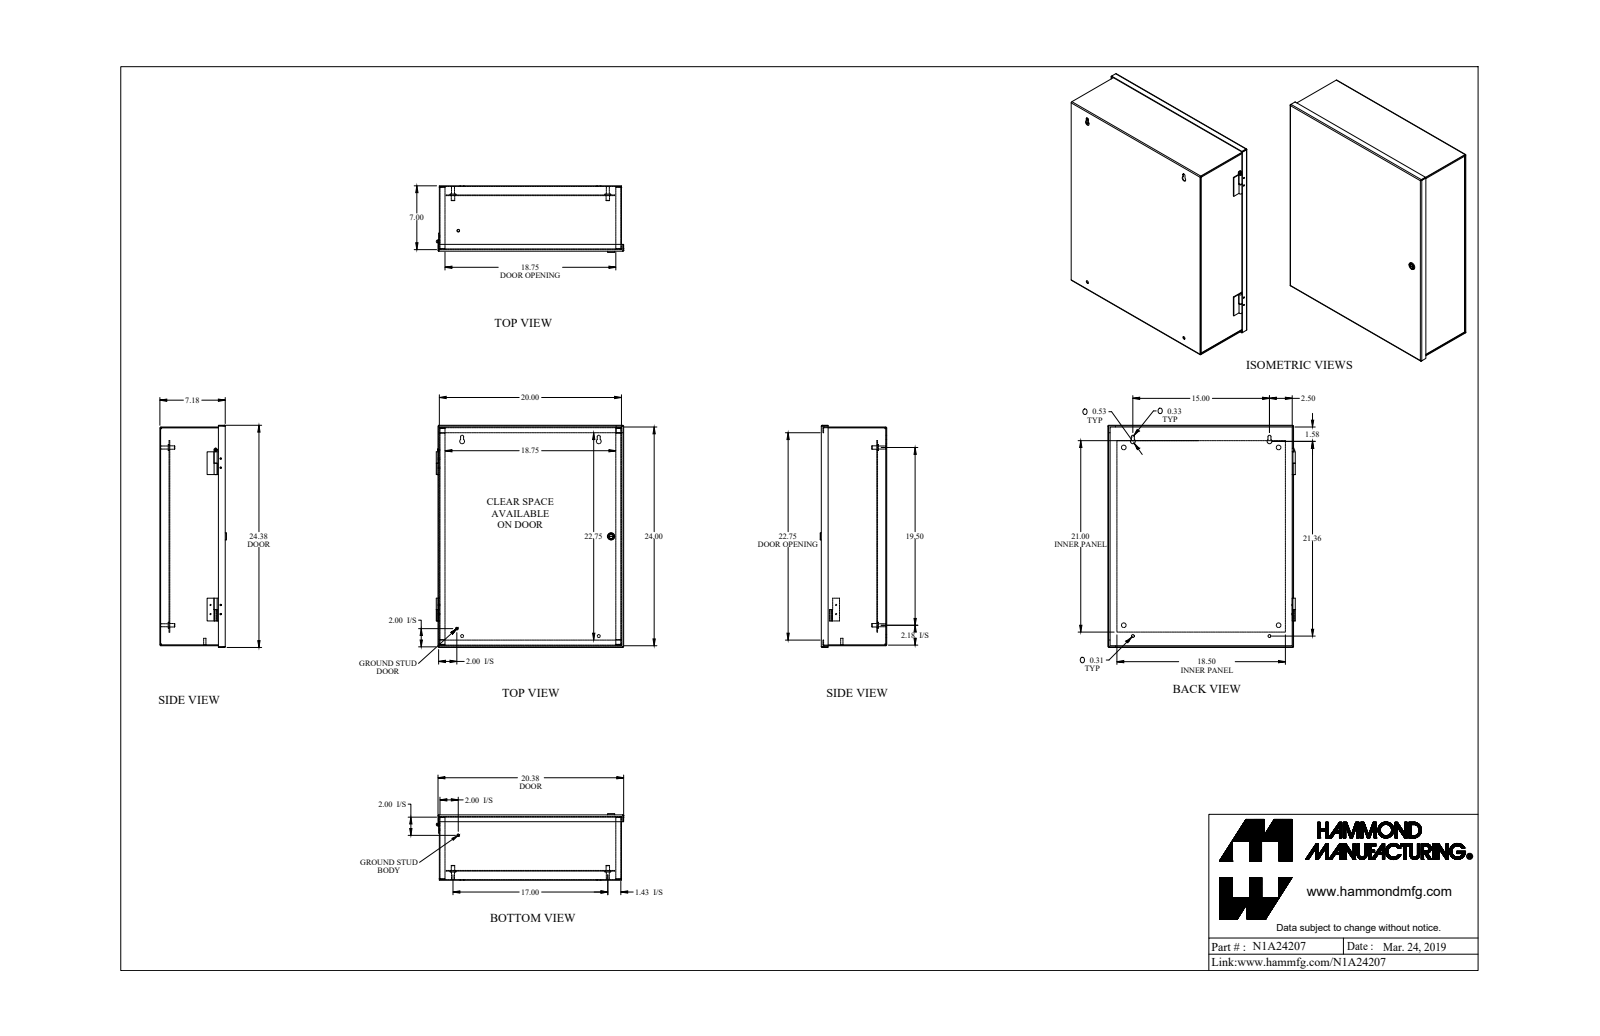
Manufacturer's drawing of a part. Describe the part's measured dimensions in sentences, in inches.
The part is named "N1A24207". Its 3-D file was written by "SolidWorks 2018 (AUTOMOTIVE_DESIGN)". It is 23 solids with 520 faces: 294 planar, 182 cylindrical and 44 other. Overall it measures 24.384 by 20.574 by 7.299 inches. Its volume is 154.5 cubic inches and its surface area 4 304 square inches. Round holes: 8 of diameter 0.14, 4 of diameter 0.5, 2 of diameter 0.307, 2 of diameter 0.312, 2 of diameter 0.445, 1 of diameter 0.17, 1 of diameter 0.187, 1 of diameter 0.516. Round bosses or shafts: 8 of diameter 0.128, 5 of diameter 0.375, 4 of diameter 0.65, 4 of diameter 0.33, 2 of diameter 1, 2 of diameter 0.281, 2 of diameter 0.25, 1 of diameter 0.788. Partial cylindrical surfaces (rounded edges, fillets, slot ends): 16 of radius 0.036, 16 of radius 0.108, 2 of radius 0.06, 2 of radius 0.153, 2 of radius 0.164, 2 of radius 0.266, 1 of radius 0.03, 1 of radius 0.125. The main face-to-face distances are 0.072, 7.105, 1.009, 6.096, 7.033, 7.177, 1.081, 6.024, 0.937, 6.168. The hole center spacings are 1, 1.119, 1.104, 1.553, 2.031, 9.757, 16.044, 16.062.
